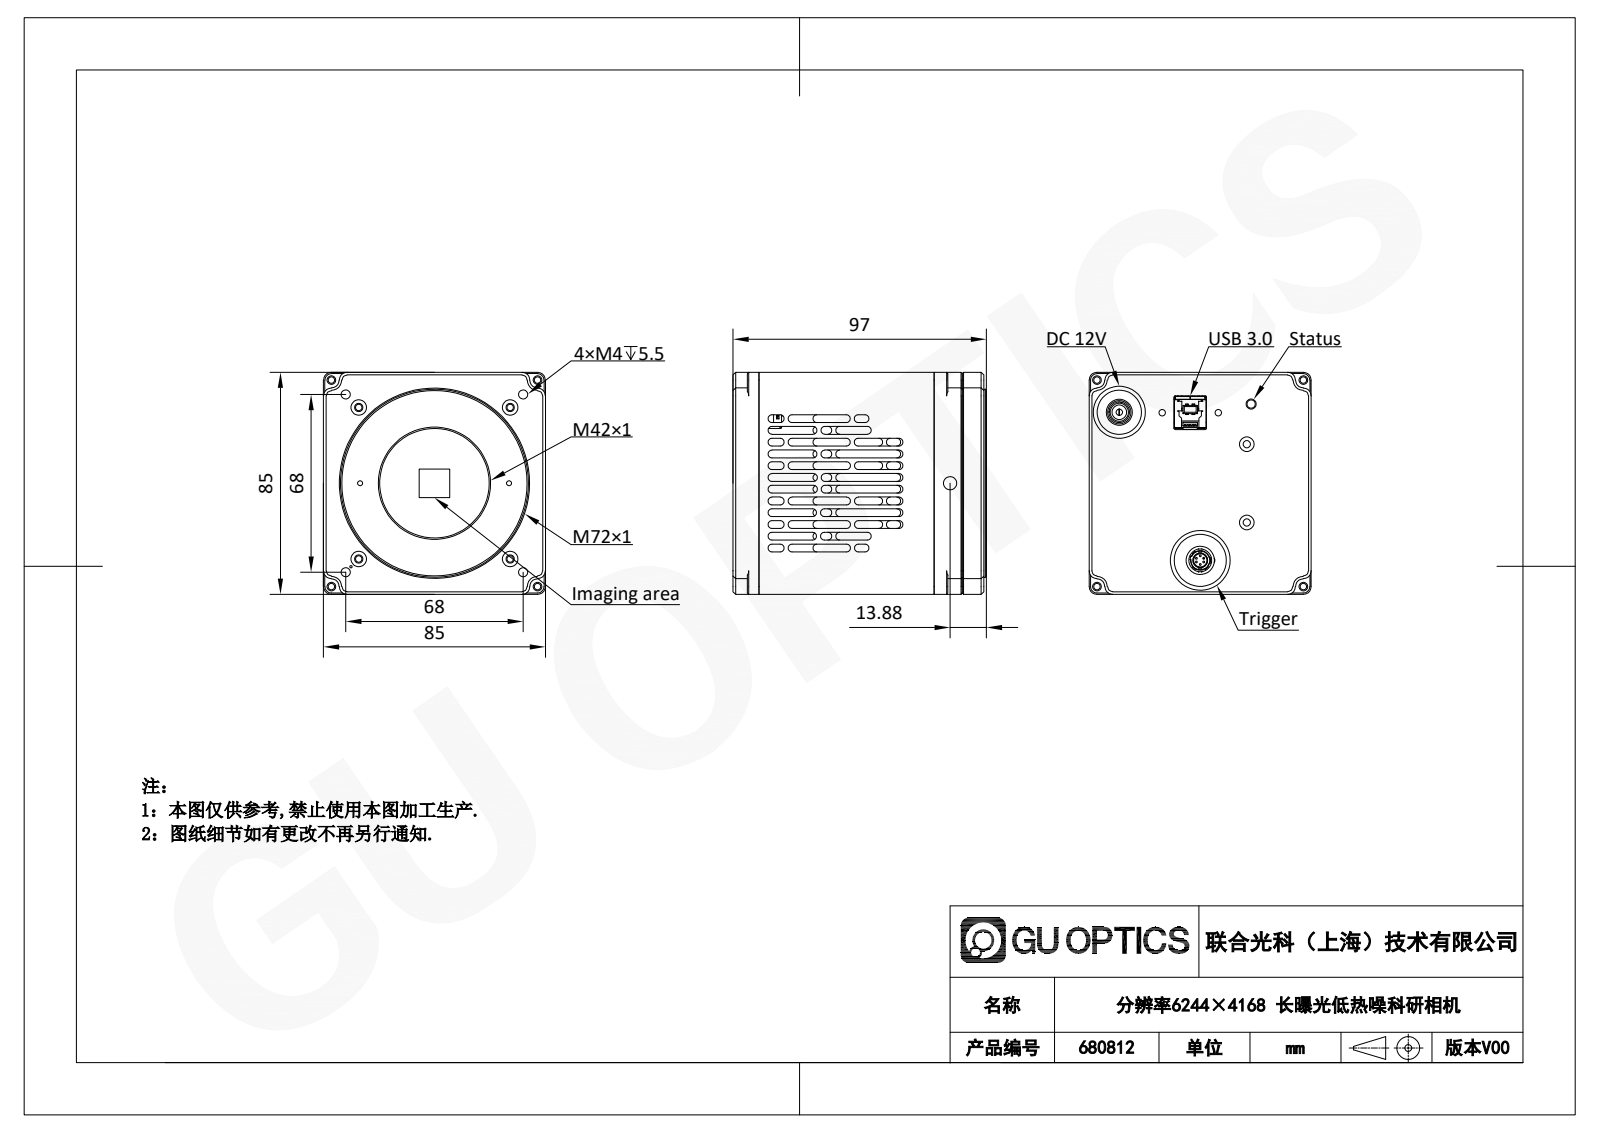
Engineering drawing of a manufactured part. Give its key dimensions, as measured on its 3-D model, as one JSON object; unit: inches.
{"part_name": "00_5_168_1; HOUSSING1_3_4_5_1_1_1_2_1; 202306080003_36; 00_5_98_1 (+8 more)", "step_written_by": "SolidWorks 2024 (CONFIG_CONTROL_DESIGN)", "units": "inches", "bodies": {"solids": 210, "faces": 2598, "planar": 1720, "cylindrical": 733, "other": 145}, "overall_size": [3.819, 3.346, 3.346], "volume_in3": 5.644, "surface_area_in2": 184.5, "round_holes": [[0.098, 10], [0.236, 8], [0.126, 4], [0.134, 4], [0.138, 4], [0.063, 3], [0.079, 3], [0.031, 2], [0.11, 2], [0.201, 2], [0.224, 2], [0.015, 1]], "round_bosses_or_shafts": [[0.039, 184], [0.118, 6], [0.028, 6], [0.157, 5], [0.098, 4], [0.031, 4], [0.433, 2], [0.047, 2]], "partial_cylinders_radius": [[0.059, 113], [0.012, 33], [0.039, 25], [0.02, 18], [0.118, 16], [0.012, 11], [0.079, 8], [0.197, 8]], "face_to_face_distances": [0.098, 3.248, 3.346, 3.15, 3.066, 0.413, 0.039, 0.463, 3.455, 0.389], "hole_center_spacings": [2.488, 2.728, 2.902, 1.142, 0.278, 0.306, 0.585, 1.356]}
